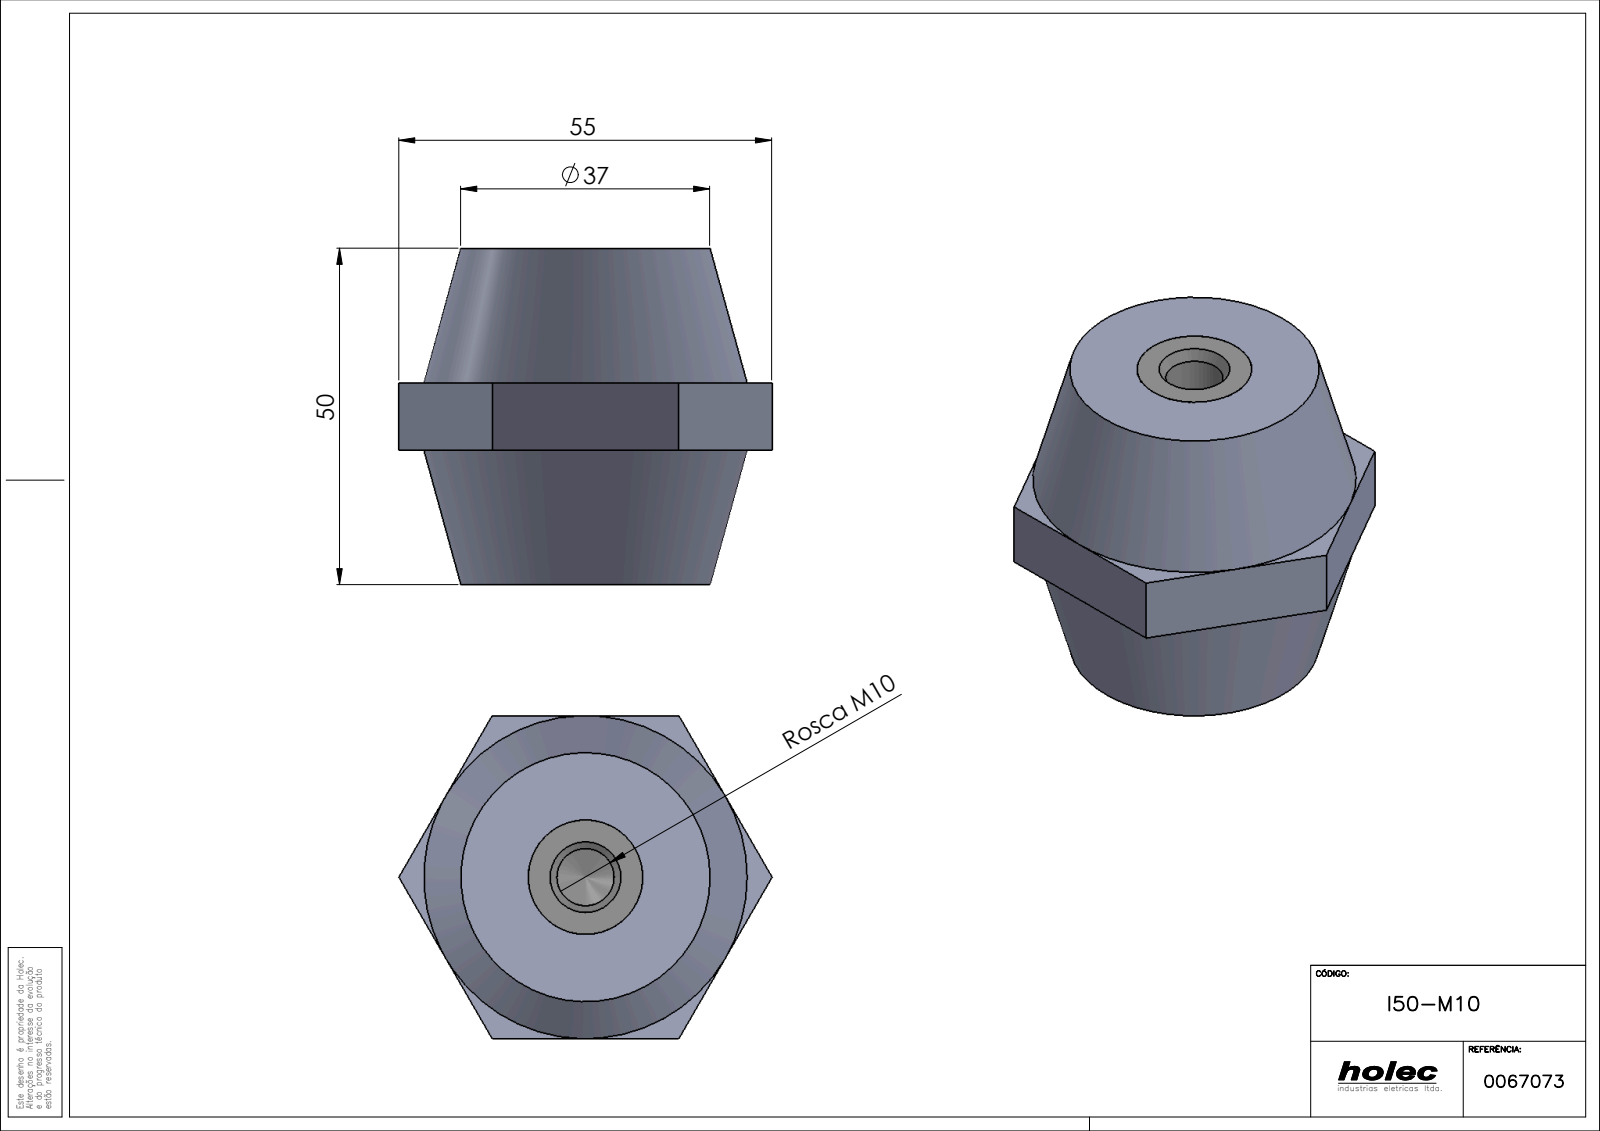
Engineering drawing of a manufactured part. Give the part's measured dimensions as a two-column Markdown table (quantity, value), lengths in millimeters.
| quantity | value |
| --- | --- |
| part name | PB1_0002; I50-M10; PB1_0106(PB1_0106_10) |
| STEP written by | SolidWorks 2017 (AUTOMOTIVE_DESIGN) |
| units | millimeters |
| bodies | 3 solids, 162 faces (82 planar, 12 cylindrical, 68 other) |
| overall size | 55.43 × 50 × 48 |
| volume | 75 295 mm³ |
| surface area | 15 770 mm² |
| round holes (diameter × count) | 8.5 × 1, 14 × 1 |
| main face-to-face distances | 17, 50, 33.01, 48, 33, 12, 5, 16.99, 16.01, 28.01 |
